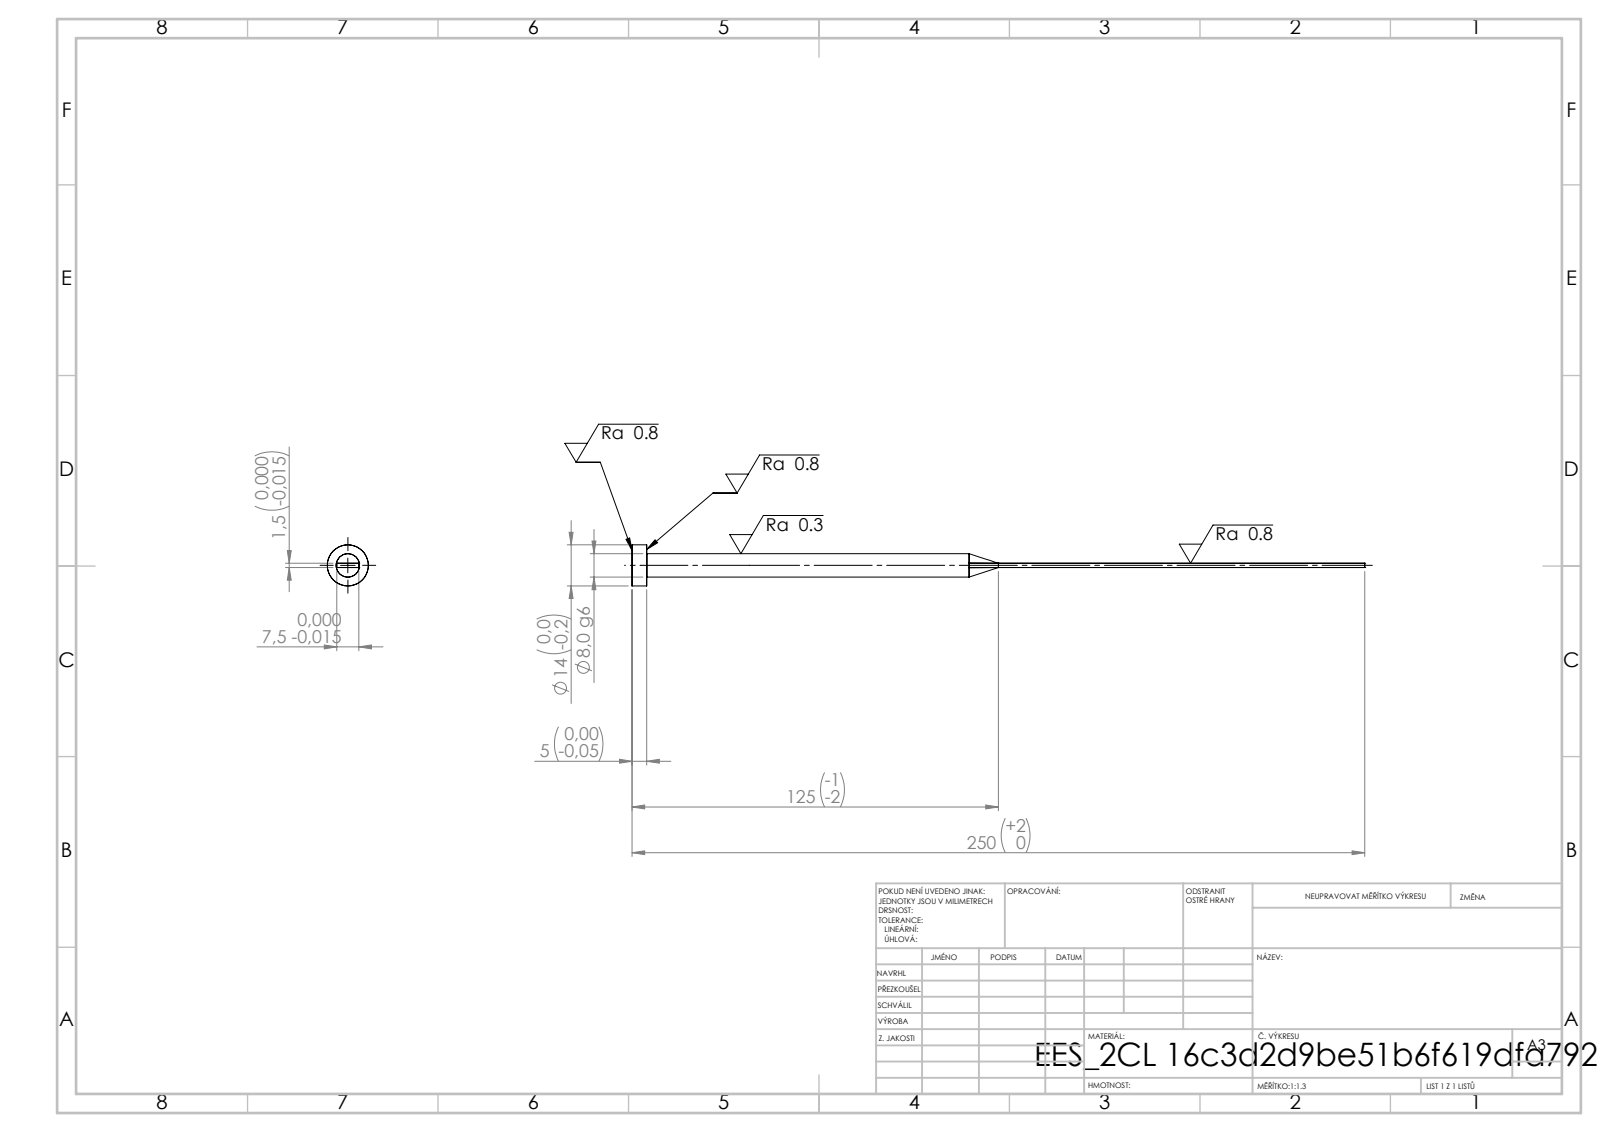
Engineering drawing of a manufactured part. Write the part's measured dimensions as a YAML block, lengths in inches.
step_written_by: "SolidWorks 2019 (CONFIG_CONTROL_DESIGN)"
units: inches
bodies: {solids: 1, faces: 15, planar: 7, cylindrical: 4, other: 4}
overall_size: [9.843, 0.551, 0.551]
volume: 0.488
surface_area: 8.857
round_bosses_or_shafts:
  - {diameter: 0.551, count: 1}
  - {diameter: 0.315, count: 1}
face_to_face_distances: [0.059, 0.295, 0.197, 9.843, 9.646]
